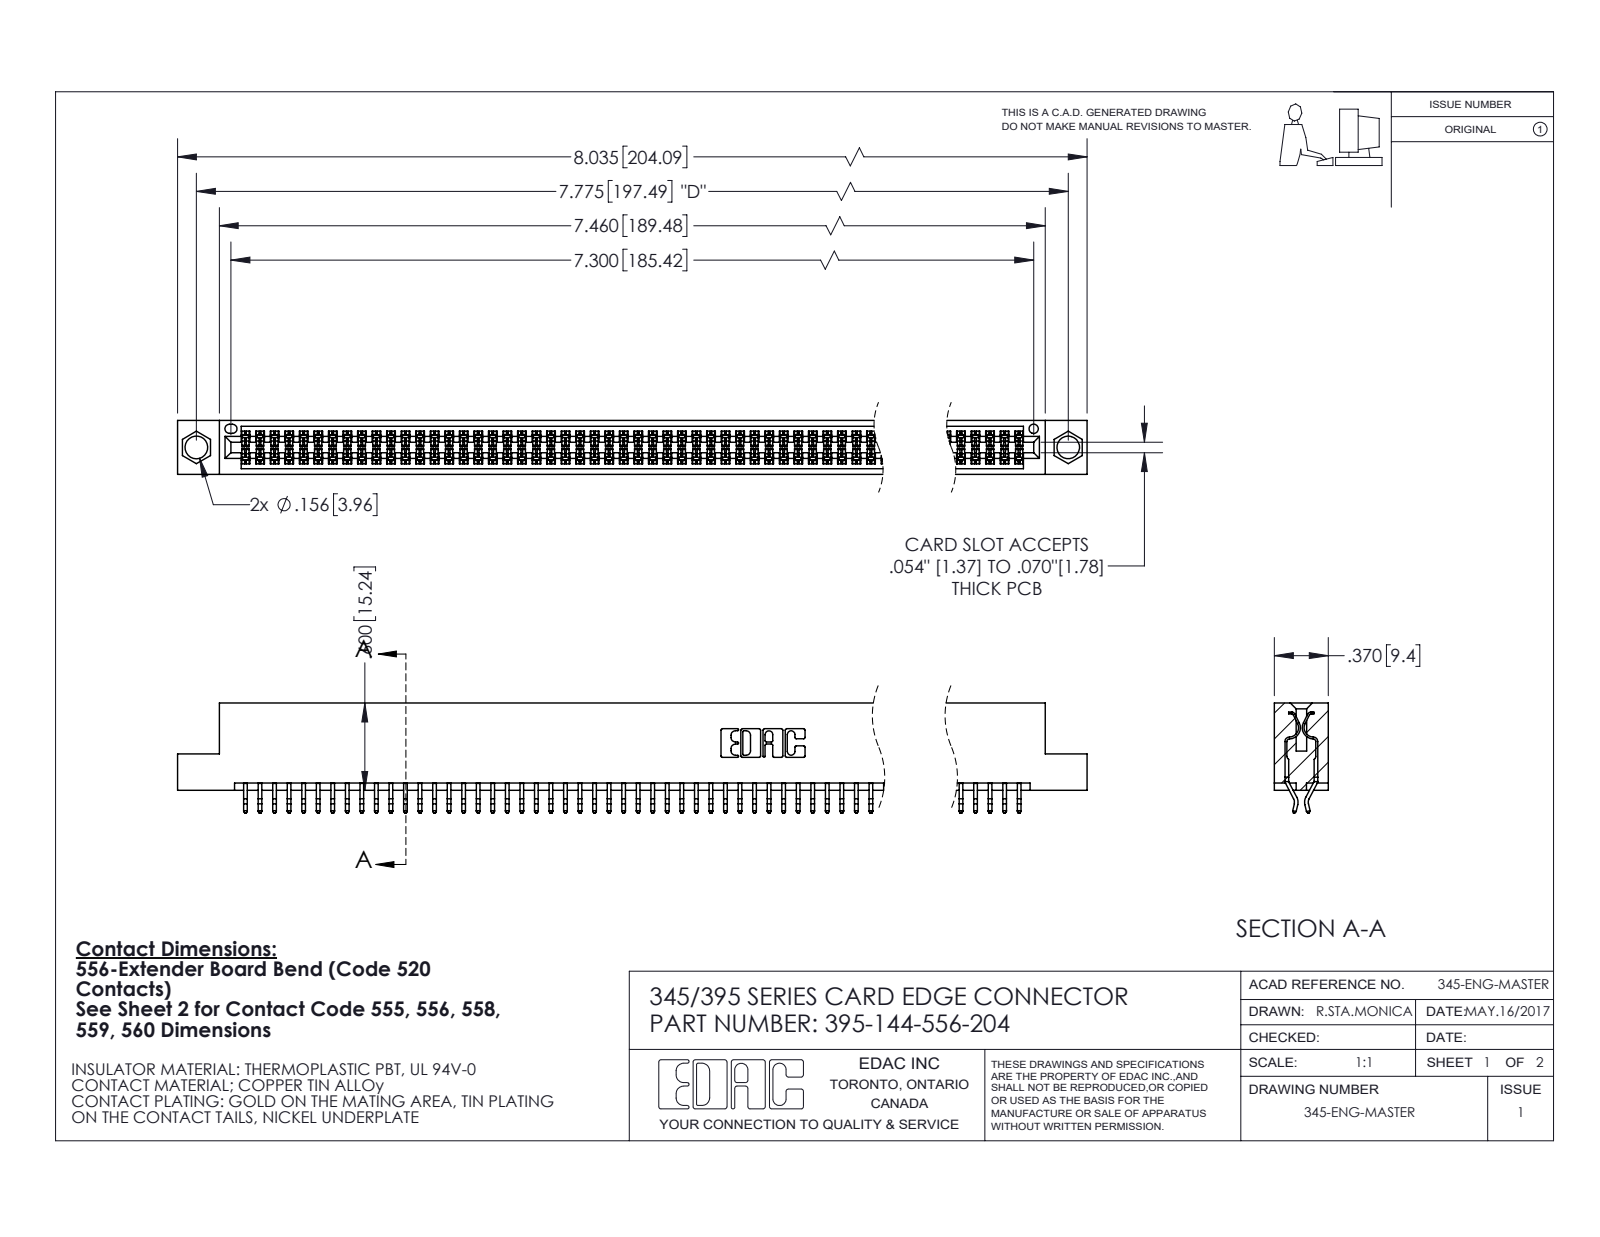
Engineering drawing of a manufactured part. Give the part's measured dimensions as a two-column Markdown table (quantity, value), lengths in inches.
| quantity | value |
| --- | --- |
| part name | 345-292-001_556 Tail; 395-144-556-204; 345 Part_Flush Mounting Lugs - 0.156 Dia-TI |
| STEP written by | SolidWorks 2020 (CONFIG_CONTROL_DESIGN) |
| units | inches |
| bodies | 145 solids, 8204 faces (5422 planar, 2782 cylindrical, 0 other) |
| overall size | 8.035 × 0.757 × 0.37 |
| volume | 1.22 in³ |
| surface area | 46.28 in² |
| round holes (diameter × count) | 0.156 × 2, 0.064 × 1 |
| partial cylindrical surfaces (radius × count) | 0.006 × 288, 0.01 × 22, 0.007 × 6, 0.031 × 6, 0.026 × 3, 0.01 × 2, 0.014 × 2, 0.019 × 2 |
| main face-to-face distances | 0.298, 0.072, 0.37, 0.2, 0.025, 0.098, 0.272, 0.225, 0.175, 0.149 |
| hole center spacings | 0.27, 7.539, 7.775 |
